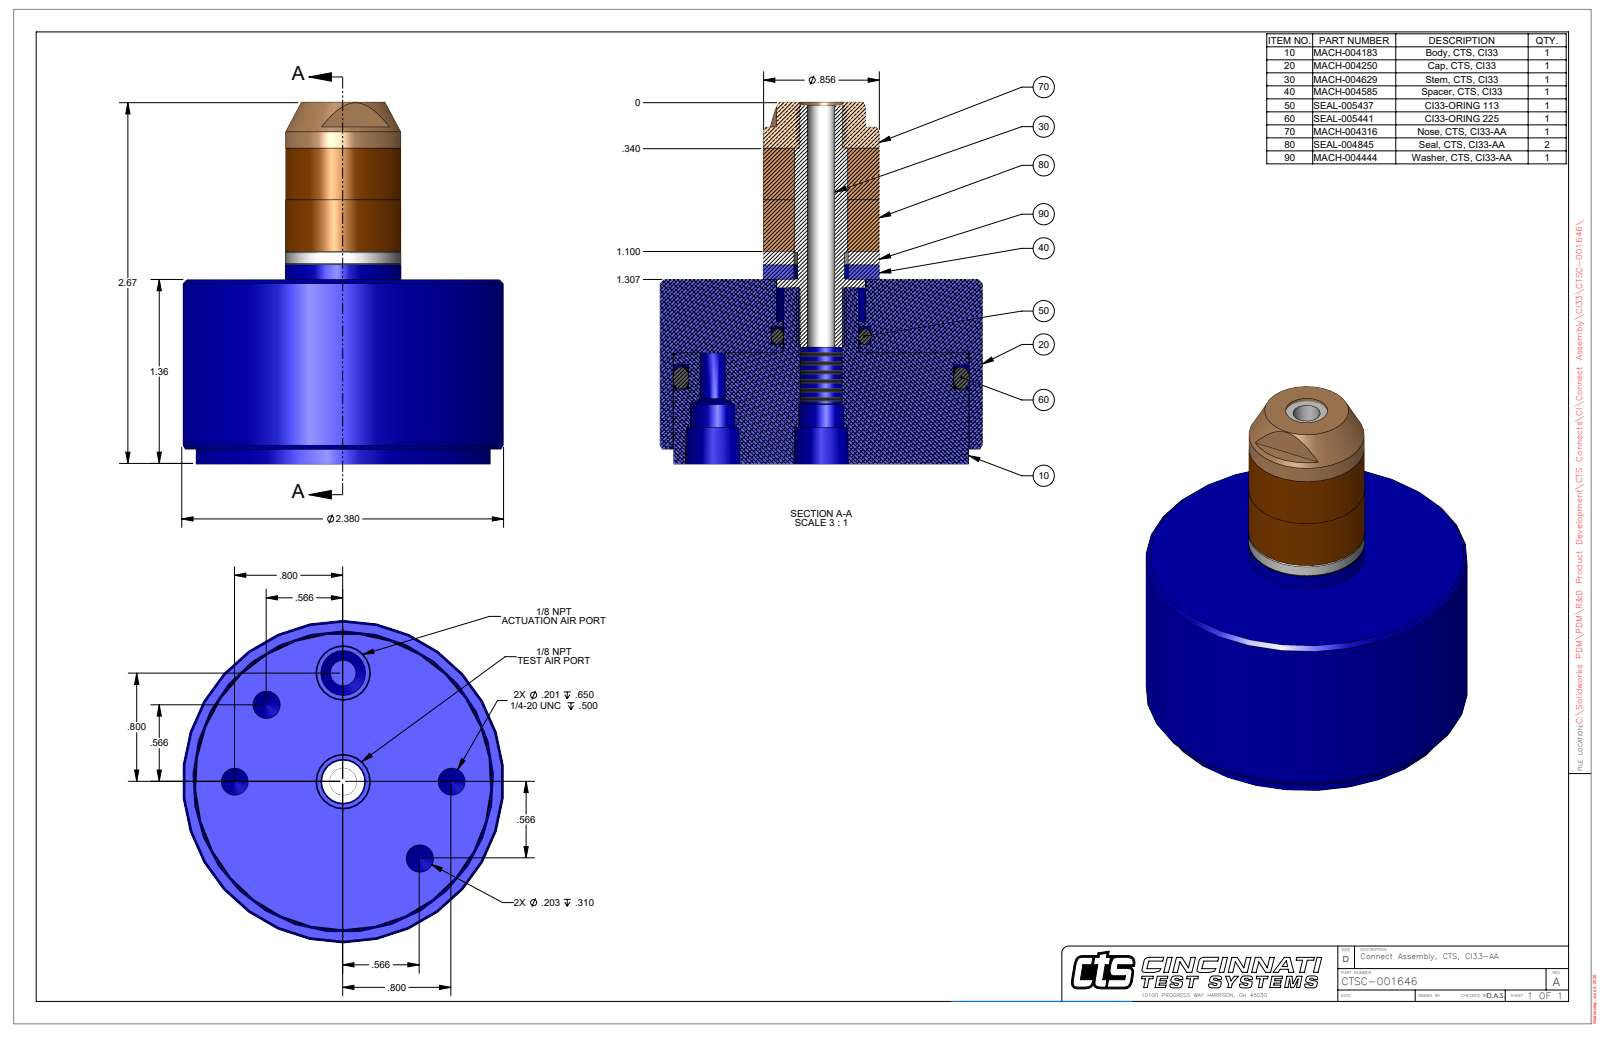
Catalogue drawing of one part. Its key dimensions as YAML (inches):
part_name: "CTSC-001646"
step_written_by: "SolidWorks 2023 (AUTOMOTIVE_DESIGN)"
units: inches
bodies: {solids: 1, faces: 76, planar: 20, cylindrical: 32, other: 24}
overall_size: [2.667, 2.38, 2.38]
volume: 6.448
surface_area: 30.11
round_holes:
  - {diameter: 0.201, count: 2}
  - {diameter: 0.203, count: 2}
  - {diameter: 0.332, count: 2}
  - {diameter: 0.203, count: 1}
  - {diameter: 0.313, count: 1}
  - {diameter: 0.659, count: 1}
  - {diameter: 2.188, count: 1}
round_bosses_or_shafts:
  - {diameter: 2.38, count: 1}
  - {diameter: 2.178, count: 1}
  - {diameter: 0.858, count: 1}
  - {diameter: 0.856, count: 1}
  - {diameter: 0.65, count: 1}
face_to_face_distances: [1.36, 0.11, 1.25, 2.667, 2.557, 1.307, 0.446, 0.336, 0.914, 2.221]
hole_center_spacings: [0.8, 0.612, 1.478, 1.131, 1.6]
